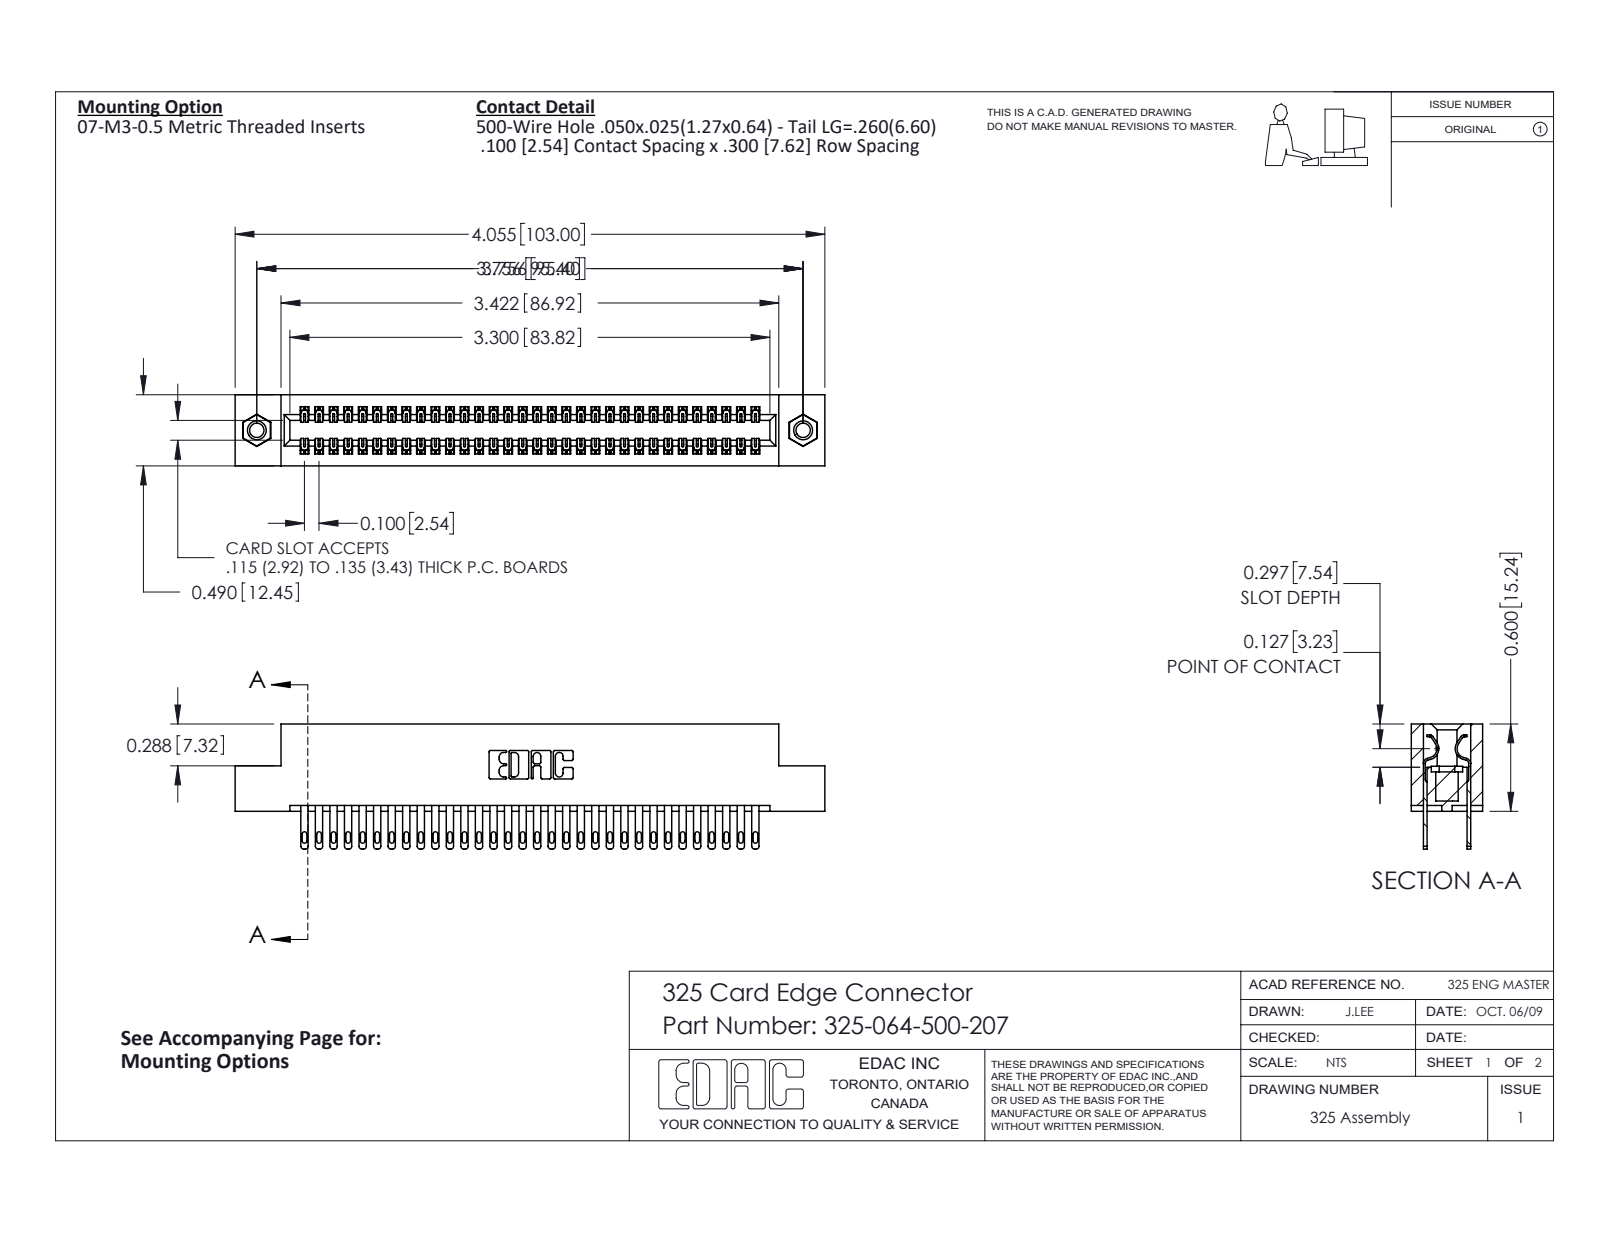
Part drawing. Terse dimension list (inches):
name: 325-064-500-207; 325 Part_TI; 345-250-001_345-250-005-103; 325-292-001_325-293-100
written by: SolidWorks 2016 (CONFIG_CONTROL_DESIGN)
unit: in
bodies: 67 solids, 3246 faces (2022 planar, 1208 cylindrical, 16 other)
size: 4.055 × 0.86 × 0.49
volume: 0.817 in³; area: 25.83 in²
holes: 2× ⌀0.098, 2× ⌀0.125, 2× ⌀0.16
bosses: 2× ⌀0.155
rounds: 96× R0.006, 64× R0.016, 64× R0.02, 22× R0.01, 6× R0.007, 6× R0.031, 3× R0.026, 2× R0.014
face distances: 0.083, 0.407, 0.3, 0.107, 0.383, 0.025, 0.49, 0.325, 0.275, 0.04
hole spacings: 3.756
